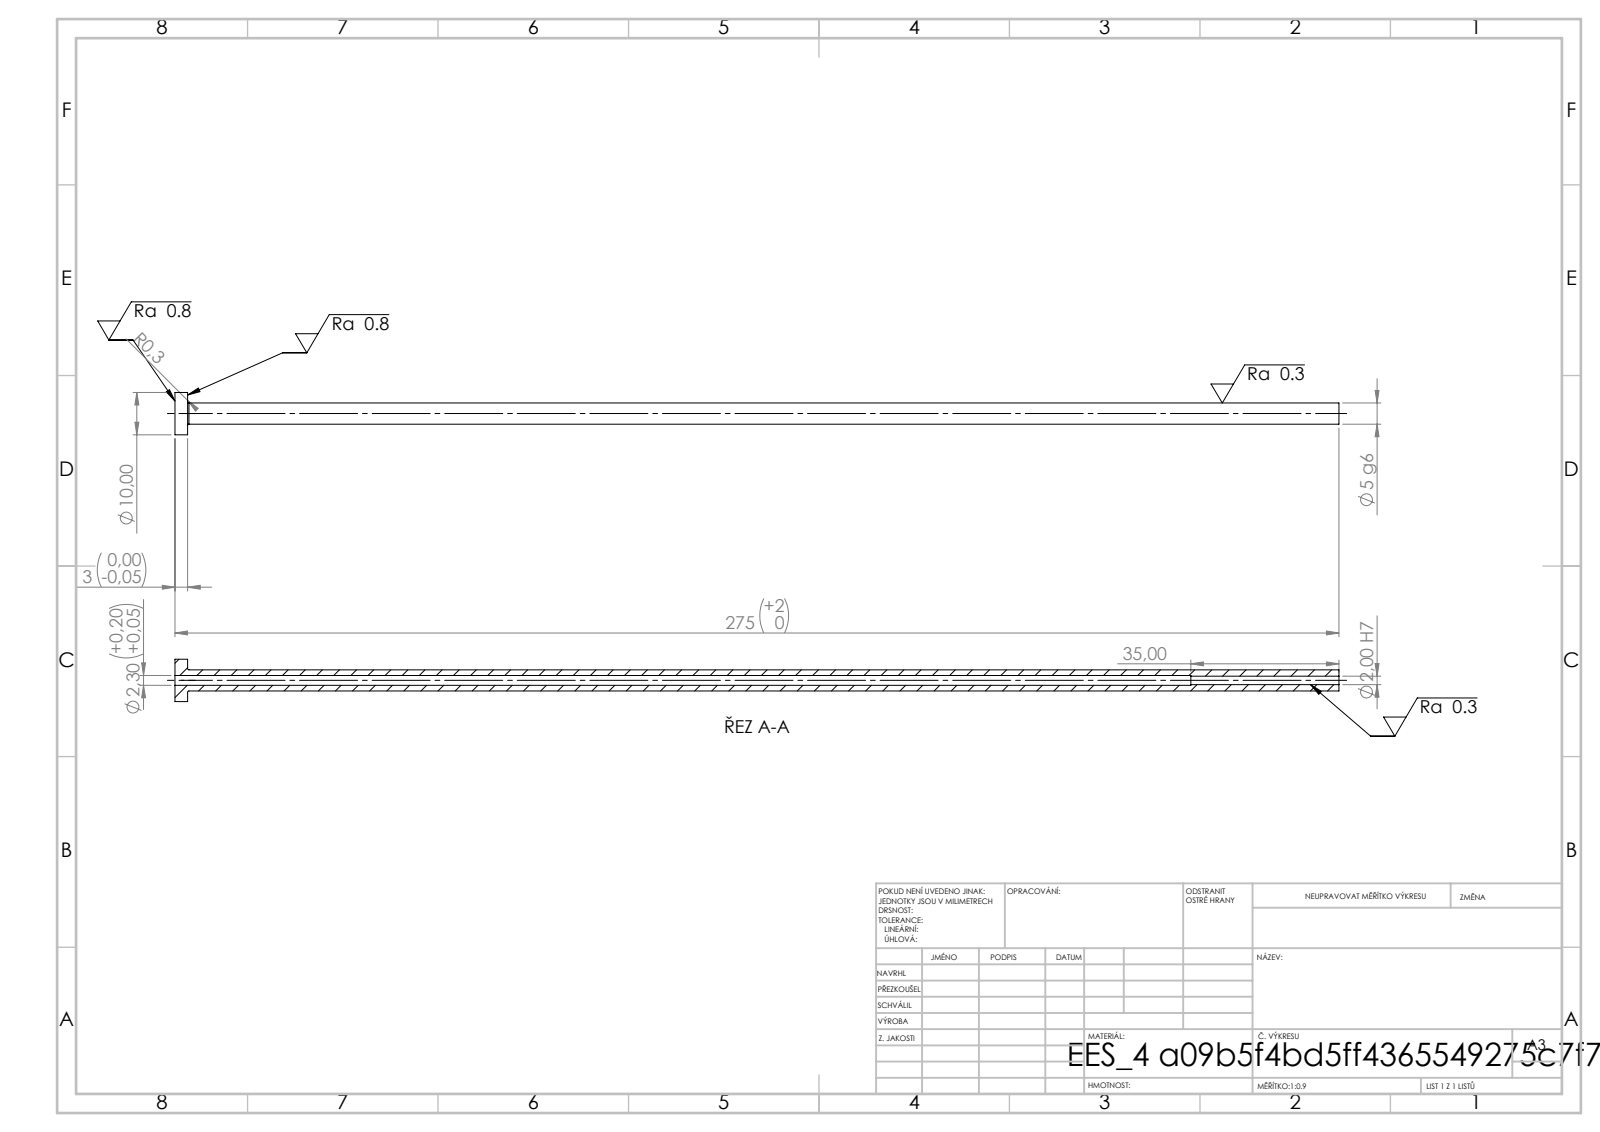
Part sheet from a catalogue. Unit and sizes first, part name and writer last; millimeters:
Units: millimetres
Overall size (bounding box): 275 × 10 × 10
Round holes (diameter × count): ⌀2 ×1, ⌀2.3 ×1
Round bosses / shafts (diameter × count): ⌀10 ×1, ⌀5 ×1
Main face-to-face distances: 3, 275, 272, 240, 237, 35
Volume: 4 470 mm³ · Surface area: 6 470 mm²
Bodies: 1 solid, 14 faces (4 planar, 8 cylindrical, 2 other)
STEP written by: SolidWorks 2019 (CONFIG_CONTROL_DESIGN)
